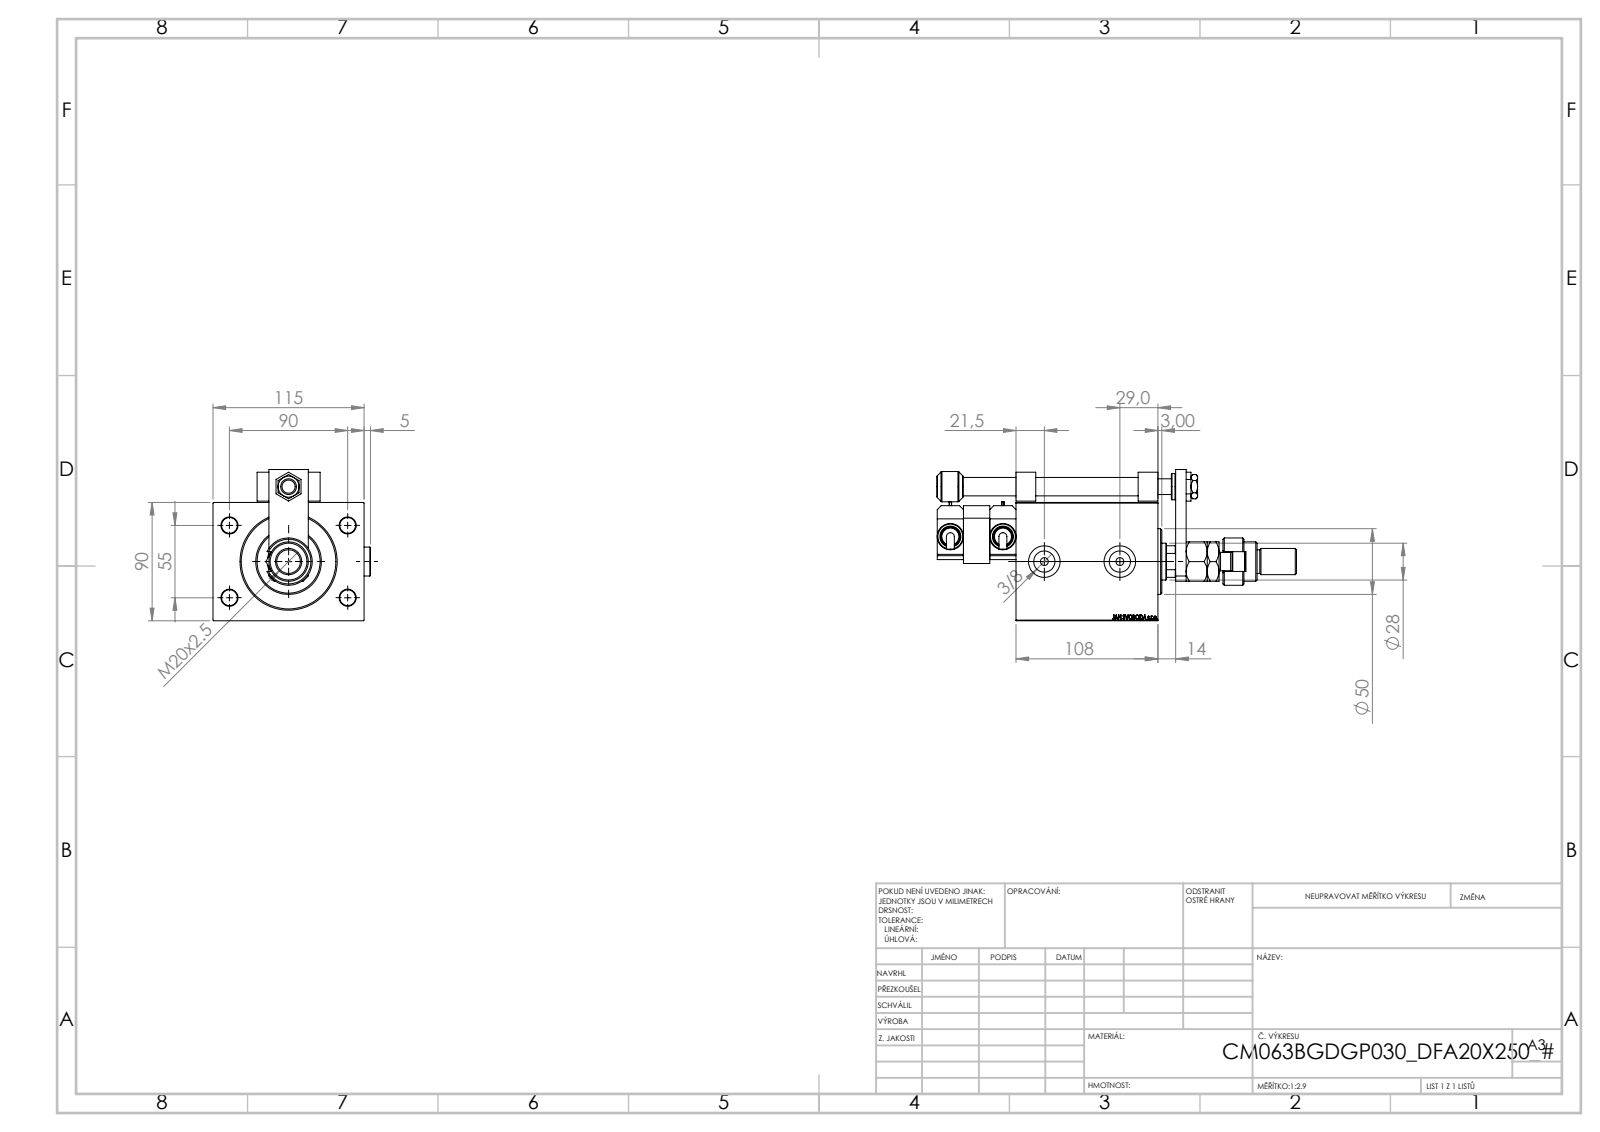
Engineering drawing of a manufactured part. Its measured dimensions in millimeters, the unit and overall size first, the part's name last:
Units: millimetres
Overall size (bounding box): 273.8 × 119.9 × 115
Round holes (diameter × count): ⌀12 ×5, ⌀4 ×4, ⌀8 ×4, ⌀6 ×2, ⌀16.17 ×2, ⌀24 ×2, ⌀13 ×1, ⌀14 ×1, ⌀18.5 ×1, ⌀20 ×1, ⌀28 ×1, ⌀31.5 ×1
Round bosses / shafts (diameter × count): ⌀22 ×3, ⌀20 ×3, ⌀14 ×3, ⌀16 ×2, ⌀6 ×2, ⌀50 ×1, ⌀36 ×1, ⌀30 ×1
Partial cylindrical surfaces — rounded edges, fillets, slot ends (radius × count): R3 ×1, R7.5 ×1, R12 ×1, R13.5 ×1
Main face-to-face distances: 90, 115, 108, 20, 17.5, 90.5, 37.5, 13.5, 40, 35
Hole centre spacings: 52.74, 20, 53.81, 55, 90, 93, 95.13, 95.74
Volume: 1 243 000 mm³ · Surface area: 192 249 mm²
Bodies: 18 solids, 1248 faces (576 planar, 143 cylindrical, 529 other)
Part name (STEP PRODUCT): NUT_D16; FEMALE_PART_FOR_DFA; V450CM_B_VCP; SWITCH_P_FRONT_BACK (+7 more)
STEP written by: SolidWorks 2019 (CONFIG_CONTROL_DESIGN)
